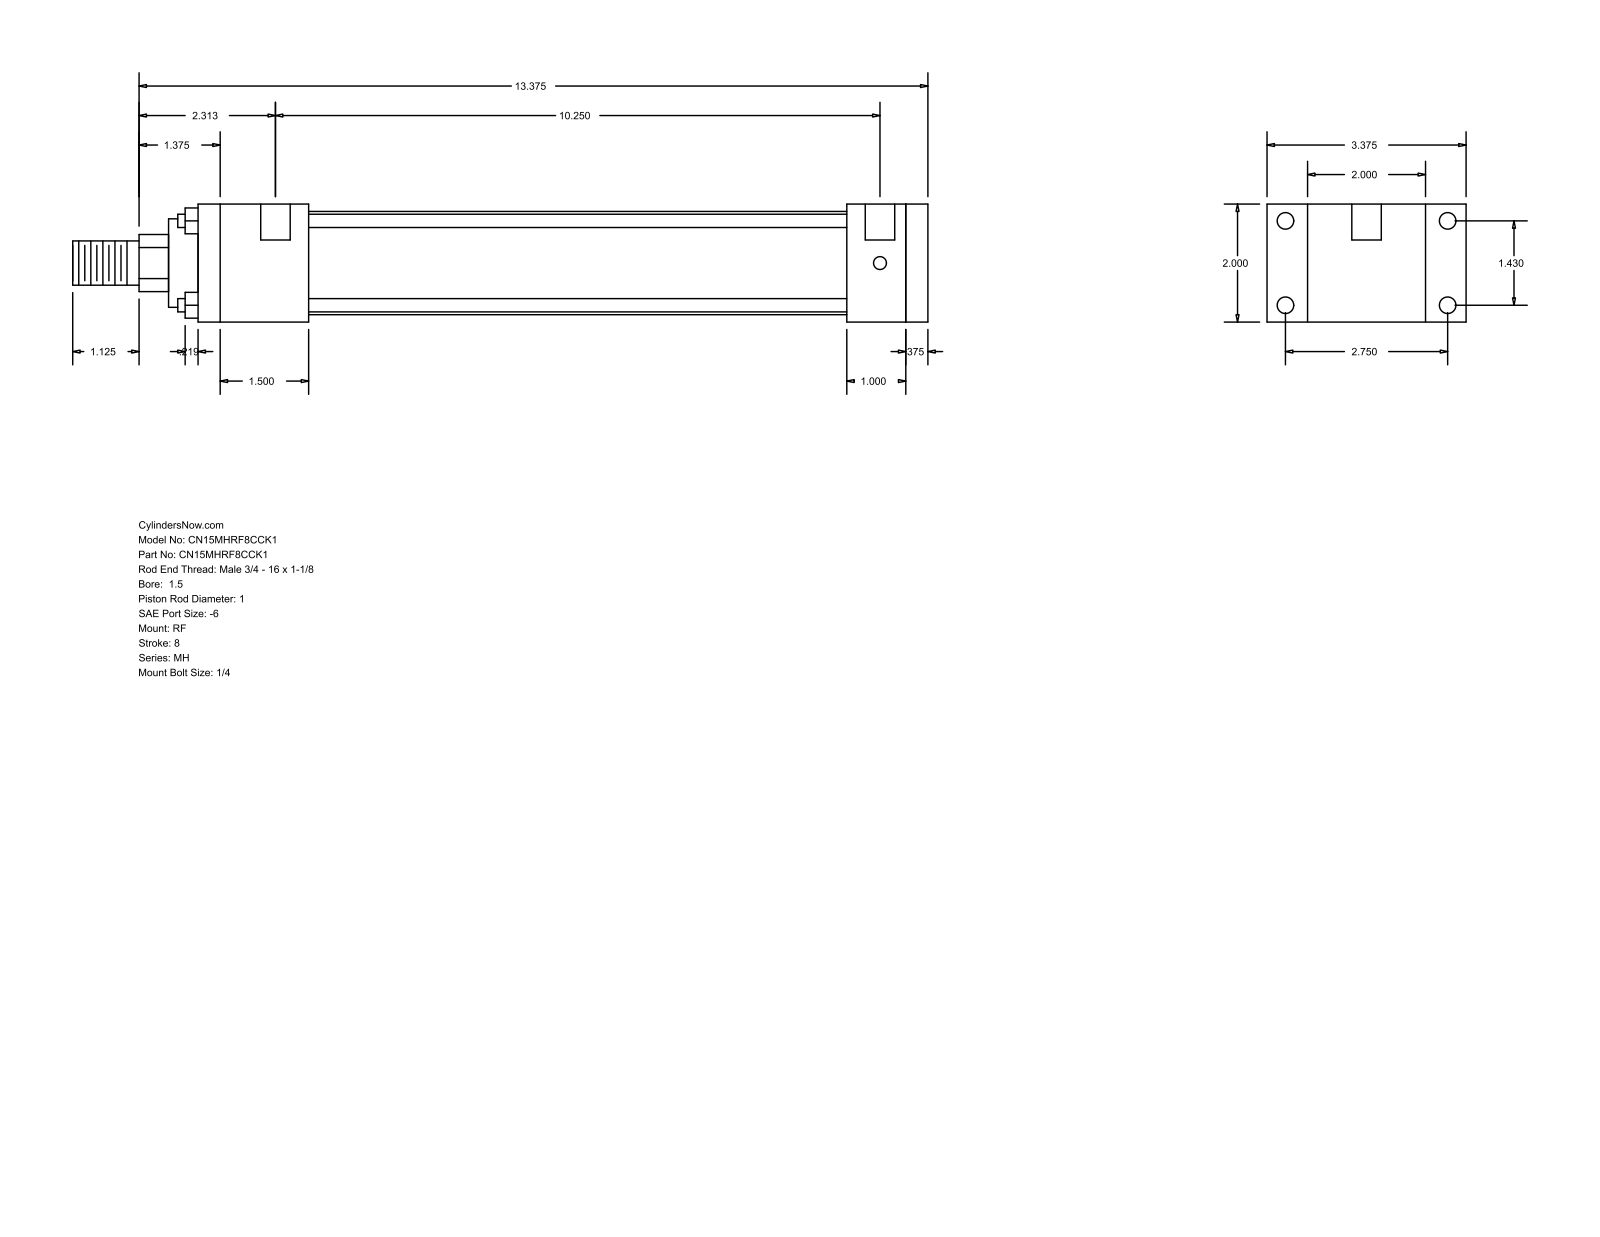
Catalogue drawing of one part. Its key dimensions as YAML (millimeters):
part_name: "MH_RF__0150_1"
step_written_by: "GSSL Pune (CONFIG_CONTROL_DESIGN)"
units: millimeters
bodies: {solids: 0, faces: 92, planar: 64, cylindrical: 28, other: 0}
overall_size: [368.3, 85.72, 50.8]
round_holes:
  - {diameter: 5.56, count: 4}
  - {diameter: 7.14, count: 4}
  - {diameter: 12.7, count: 2}
round_bosses_or_shafts:
  - {diameter: 5.71, count: 4}
  - {diameter: 44.45, count: 1}
  - {diameter: 38.1, count: 1}
  - {diameter: 25.4, count: 1}
  - {diameter: 19.05, count: 1}
partial_cylinders:
  - {radius: 12.29, count: 1}
face_to_face_distances: [50.8, 9.53, 304.8, 25.4, 314.33, 17.46, 68.26, 279.4, 34.93, 47.63]
hole_center_spacings: [36.32, 69.84, 78.72, 263.53, 3.18, 260.35]
